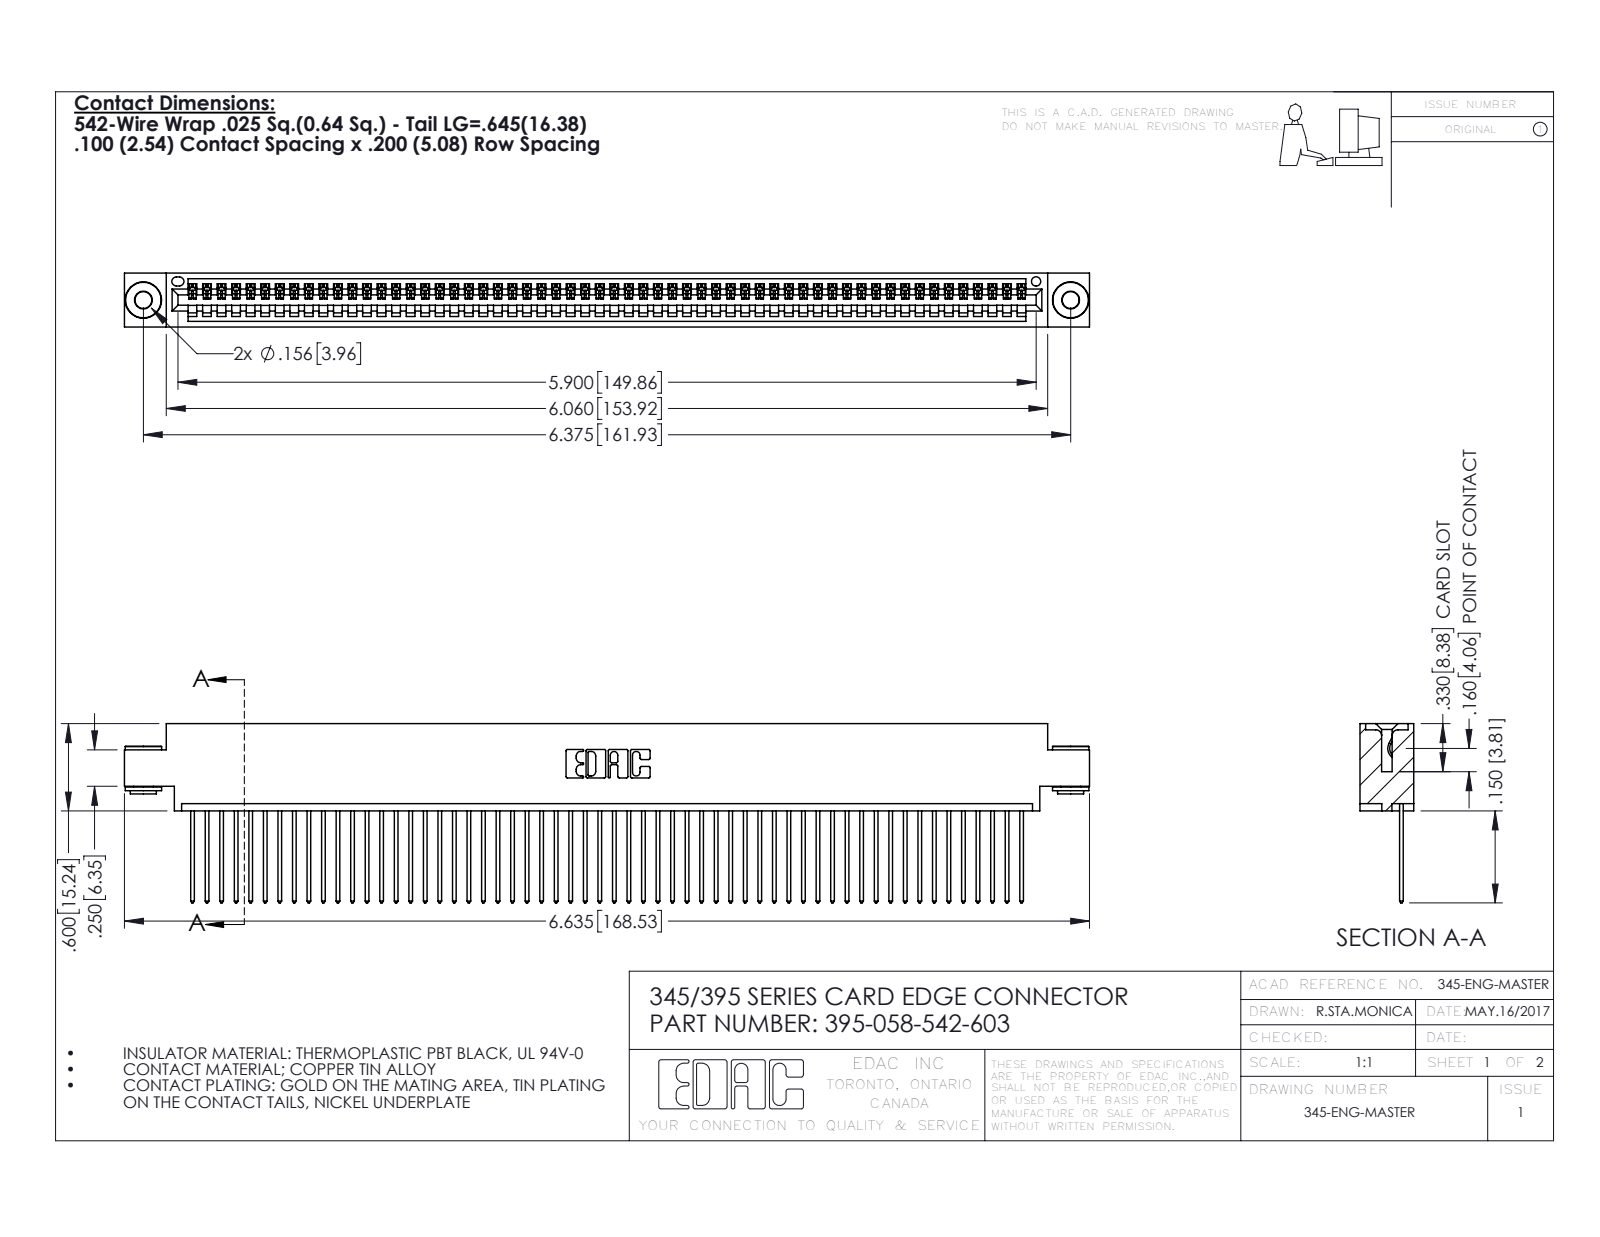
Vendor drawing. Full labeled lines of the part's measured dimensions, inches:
Part name (STEP PRODUCT): 345-292-001_345-293-142; 345 Part_0.170 Offset - 0.156 Dia-TH; 395-058-542-603; 345-250-002_345-250-002-102
STEP written by: SolidWorks 2016 (CONFIG_CONTROL_DESIGN)
Units: inches
Bodies: 61 solids, 3532 faces (2414 planar, 1110 cylindrical, 8 other)
Overall size (bounding box): 6.635 × 1.232 × 0.37
Volume: 0.987 in³ · Surface area: 35.44 in²
Round holes (diameter × count): ⌀0.116 ×2, ⌀0.156 ×2, ⌀0.064 ×1
Round bosses / shafts (diameter × count): ⌀0.25 ×2, ⌀0.18 ×2, ⌀0.136 ×2
Partial cylindrical surfaces — rounded edges, fillets, slot ends (radius × count): R0.006 ×116, R0.01 ×116, R0.01 ×22, R0.007 ×6, R0.031 ×6, R0.026 ×3, R0.031 ×2, R0.04 ×2
Main face-to-face distances: 0.072, 0.298, 0.37, 0.098, 0.272, 0.025, 0.2, 0.225, 0.175, 0.149
Hole centre spacings: 0.27, 6.139, 6.375
